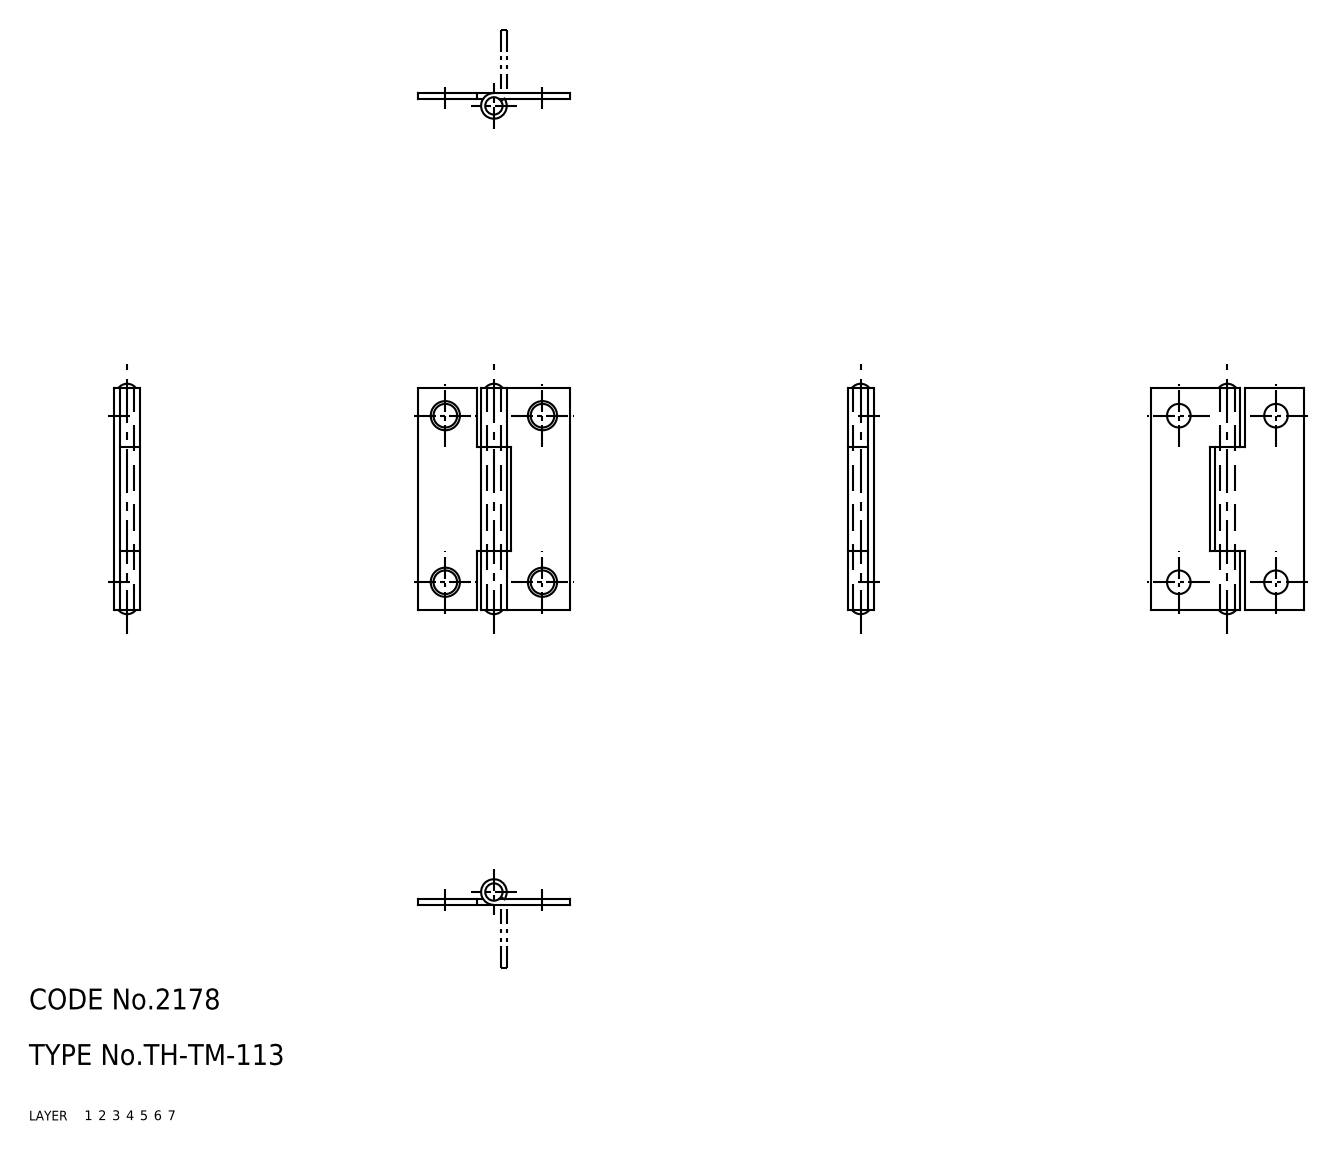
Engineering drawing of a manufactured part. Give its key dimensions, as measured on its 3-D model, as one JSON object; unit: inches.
{"part_name": "67111788; 67111801; 67111814", "step_written_by": "CADfix (AUTOMOTIVE_DESIGN)", "units": "inches", "bodies": {"solids": 3, "faces": 48, "planar": 0, "cylindrical": 0, "other": 48}, "overall_size": [1.299, 0.866, 0.146], "volume_in3": 0.047, "surface_area_in2": 3.247}
